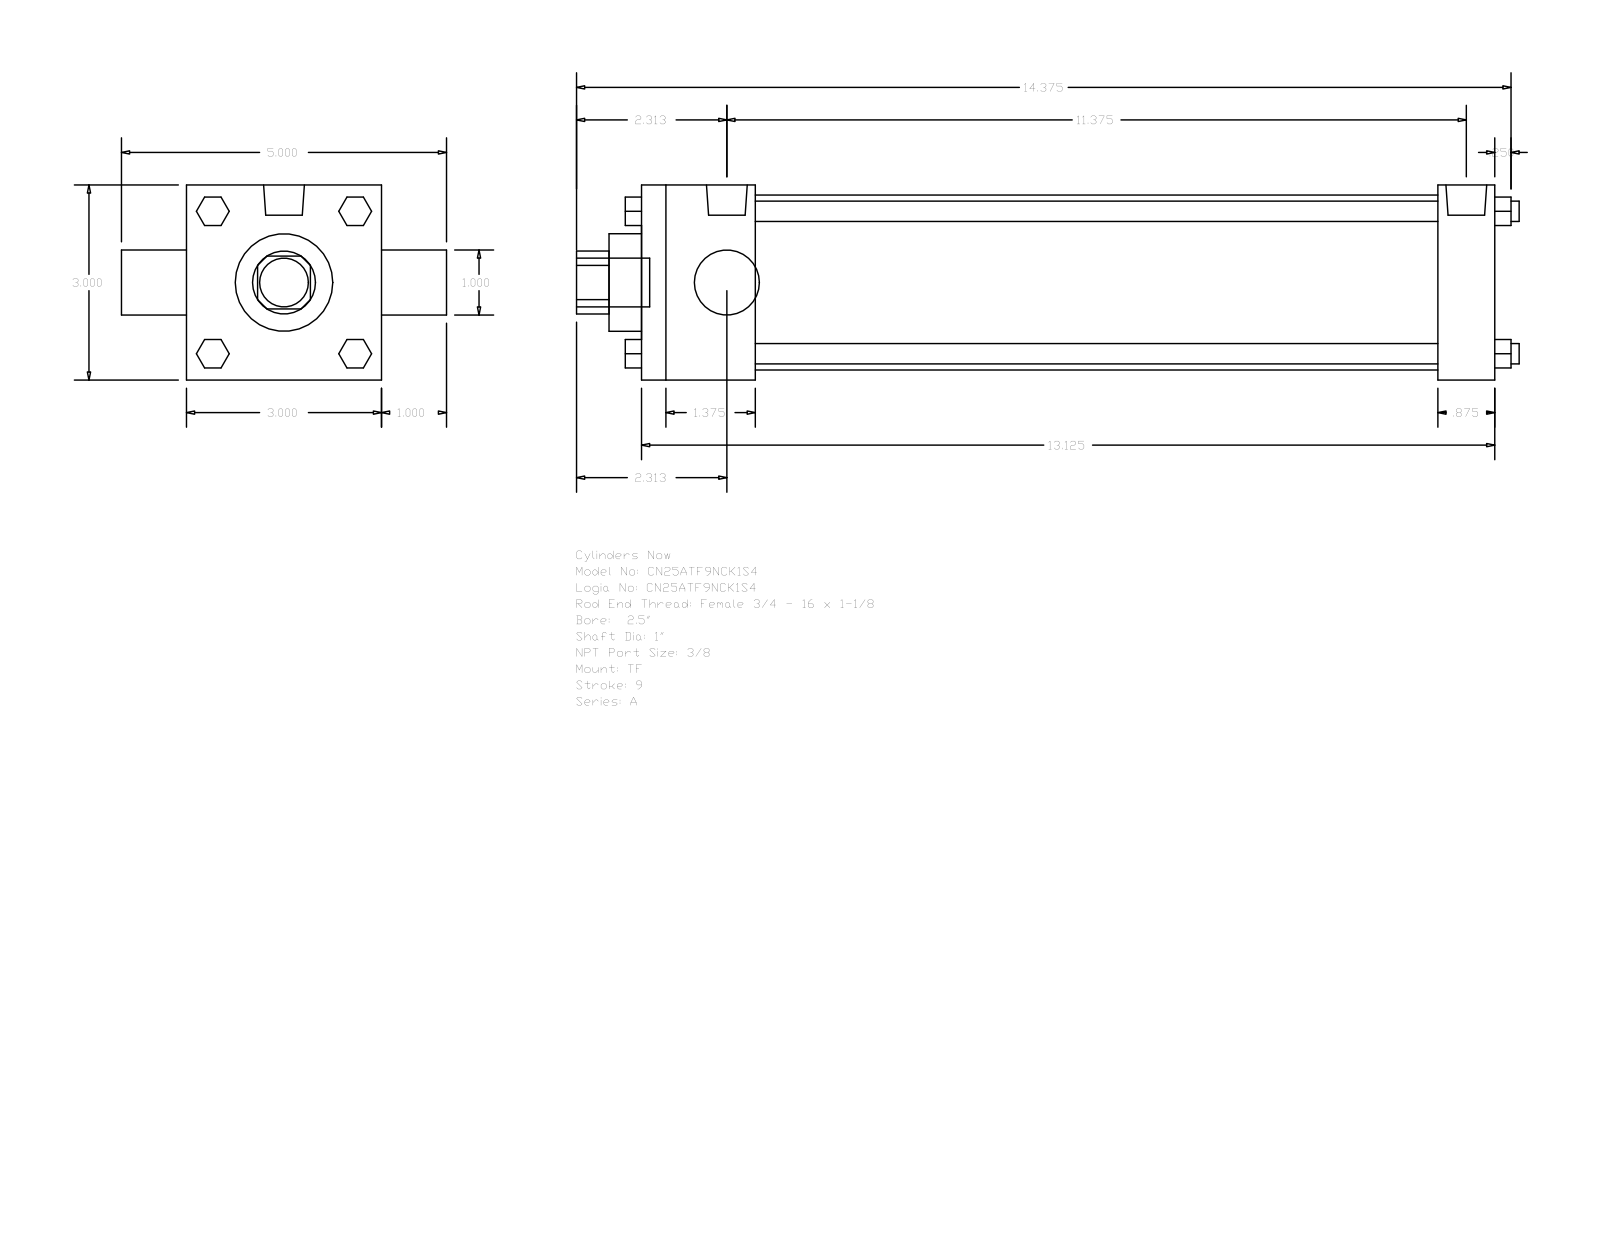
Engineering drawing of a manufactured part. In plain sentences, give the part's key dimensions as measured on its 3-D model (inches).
The part is named "A_TF__0250_1". Its 3-D file was written by "GSSL Pune (CONFIG_CONTROL_DESIGN)". It is 0 solids with 120 faces: 92 planar, 28 cylindrical and 0 other. Overall it measures 14.5 by 5 by 3 inches. Round holes: 2 of diameter 1, 1 of diameter 1.5, 1 of diameter 2.69. Round bosses or shafts: 4 of diameter 0.313, 3 of diameter 0.219, 2 of diameter 0.627, 1 of diameter 0.75. Partial cylindrical surfaces (rounded edges, fillets, slot ends): 1 of radius 0.484. The main face-to-face distances are 3, 13.125, 1.75, 12.25, 10.5, 11.375, 0.875, 1, 4, 13.625.
